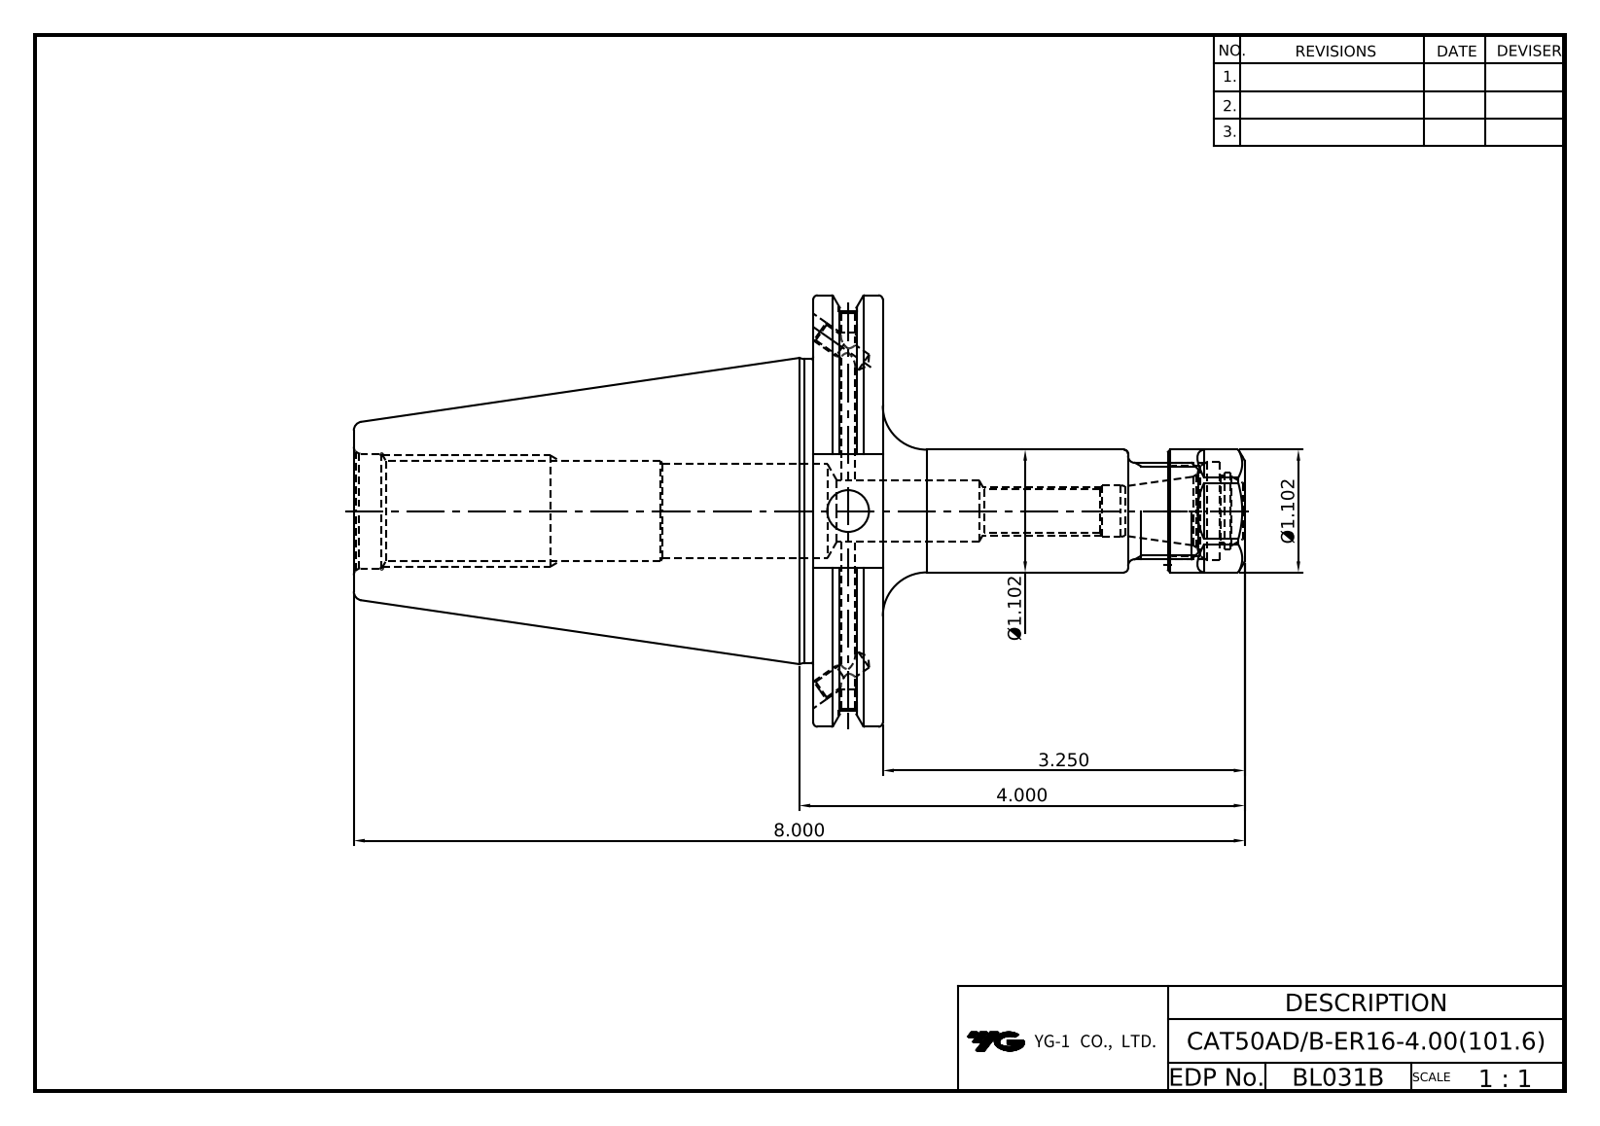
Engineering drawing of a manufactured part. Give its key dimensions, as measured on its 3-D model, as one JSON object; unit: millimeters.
{"part_name": "조립품3; LO-CAT50ADB-ER16-4.00; ER16NUT", "step_written_by": "Autodesk Inventor 2024 (AUTOMOTIVE_DESIGN)", "units": "millimeters", "bodies": {"solids": 2, "faces": 123, "planar": 56, "cylindrical": 36, "other": 31}, "overall_size": [203.2, 98.42, 94.69], "volume_mm3": 358652, "surface_area_mm2": 57590, "round_holes": [[3.24, 2], [4.13, 2], [4.2, 2], [5, 2], [1, 1], [9.14, 1], [9.53, 1], [11.8, 1], [12.8, 1], [14, 1], [17.7, 1], [20.6, 1]], "round_bosses_or_shafts": [[98.42, 1], [91.29, 1], [69.25, 1], [28, 1], [22, 1]], "partial_cylinders_radius": [[7.7, 2]], "face_to_face_distances": [15.88, 104.77, 120.65, 73.03, 25, 203.2, 98.43, 82.55, 25.9, 6], "hole_center_spacings": [12]}
